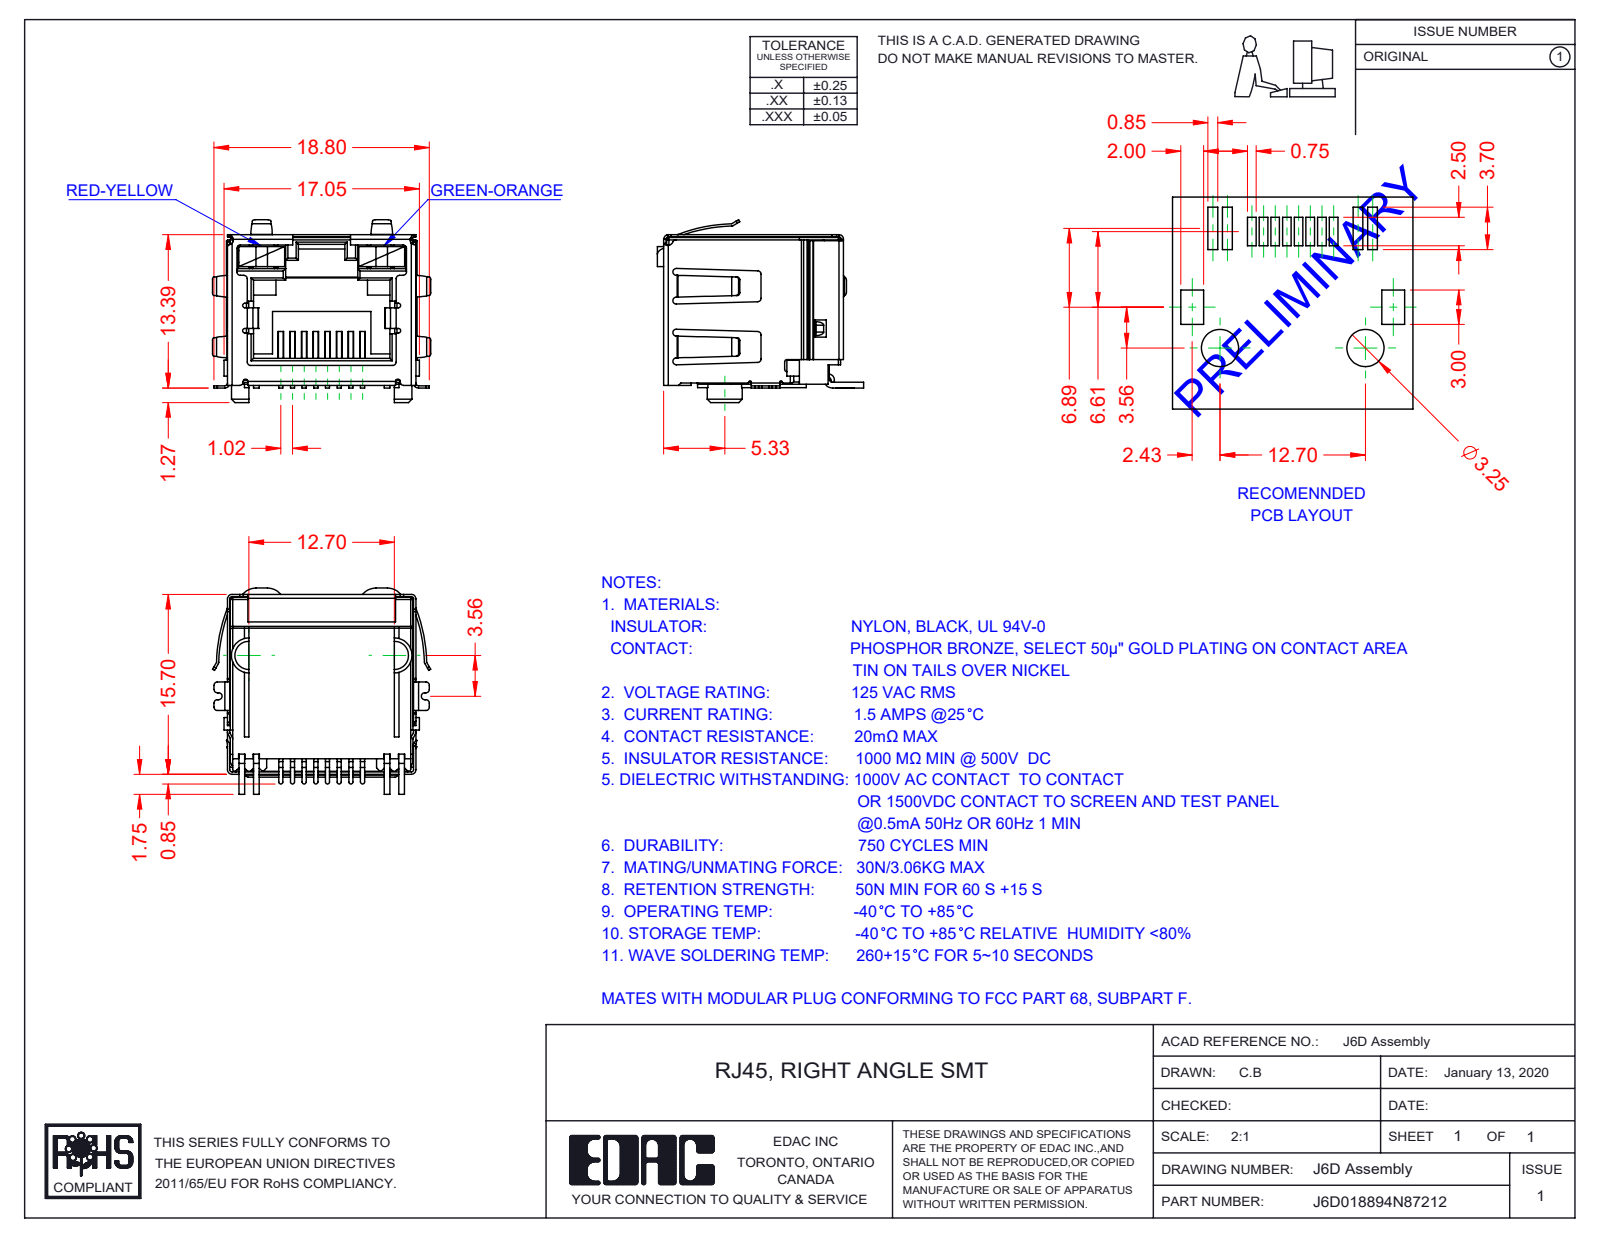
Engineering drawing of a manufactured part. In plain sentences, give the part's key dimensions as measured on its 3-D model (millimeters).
The part is named "J6D018894N87212; 6D Insulator; 6D LED LH_8-Red-Yellow; 6D Contacts (+2 more)". Its 3-D file was written by "SolidWorks 2016 (CONFIG_CONTROL_DESIGN)". It is 12 solids with 1034 faces: 703 planar, 286 cylindrical and 45 other. Overall it measures 19.06 by 18 by 15.95 millimeters. Its volume is 1 790 cubic millimeters and its surface area 4 796 square millimeters. Partial cylindrical surfaces (rounded edges, fillets, slot ends): 55 of radius 0.3, 40 of radius 0.2, 19 of radius 0.4, 16 of radius 0.25, 12 of radius 0.1, 8 of radius 0.15, 8 of radius 0.18, 6 of radius 0.5. The main face-to-face distances are 16, 16.2, 16.25, 2.25, 1, 15.95, 12.8, 0.45, 13.05, 10.6.
